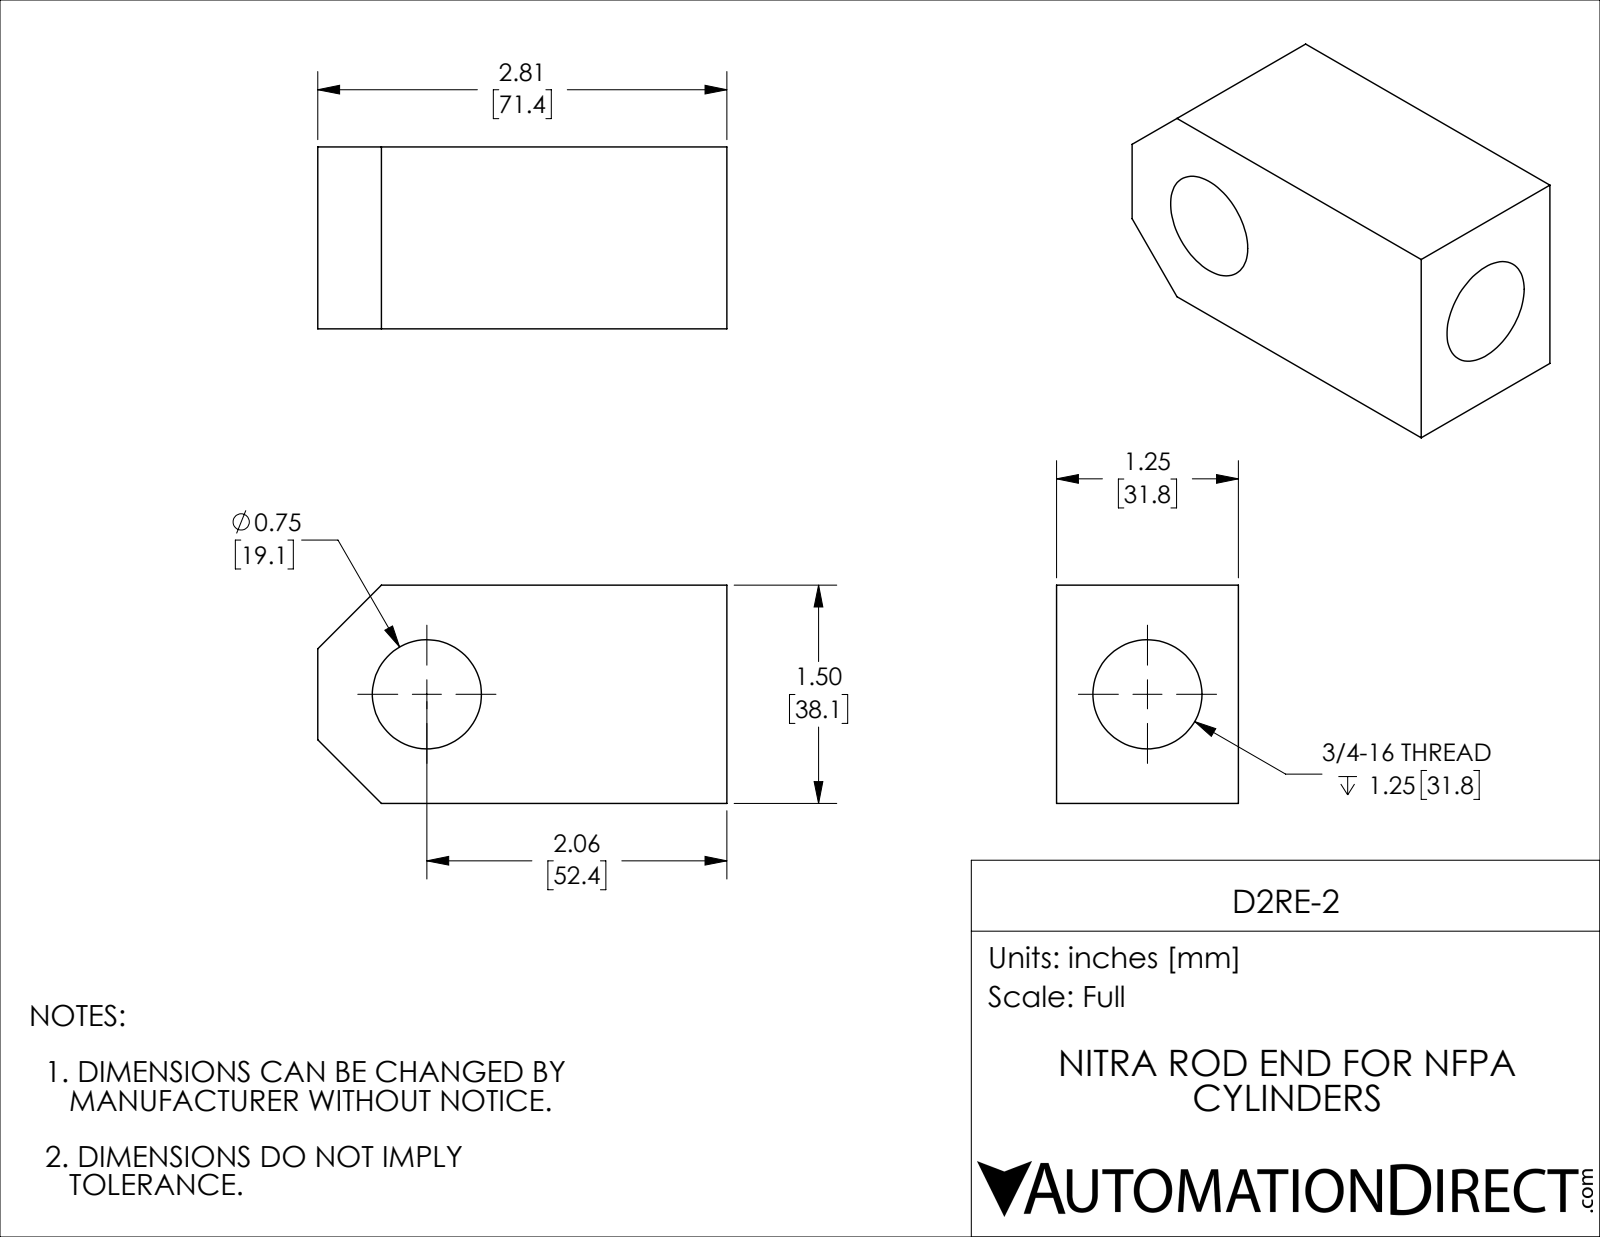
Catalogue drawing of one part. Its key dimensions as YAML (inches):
part_name: "D2RE-2"
step_written_by: "SolidWorks 2019 (CONFIG_CONTROL_DESIGN)"
units: inches
bodies: {solids: 1, faces: 14, planar: 8, cylindrical: 4, other: 2}
overall_size: [2.813, 1.5, 1.25]
volume: 3.897
surface_area: 23.28
round_holes:
  - {diameter: 0.75, count: 2}
face_to_face_distances: [1.25, 1.5, 2.813]
